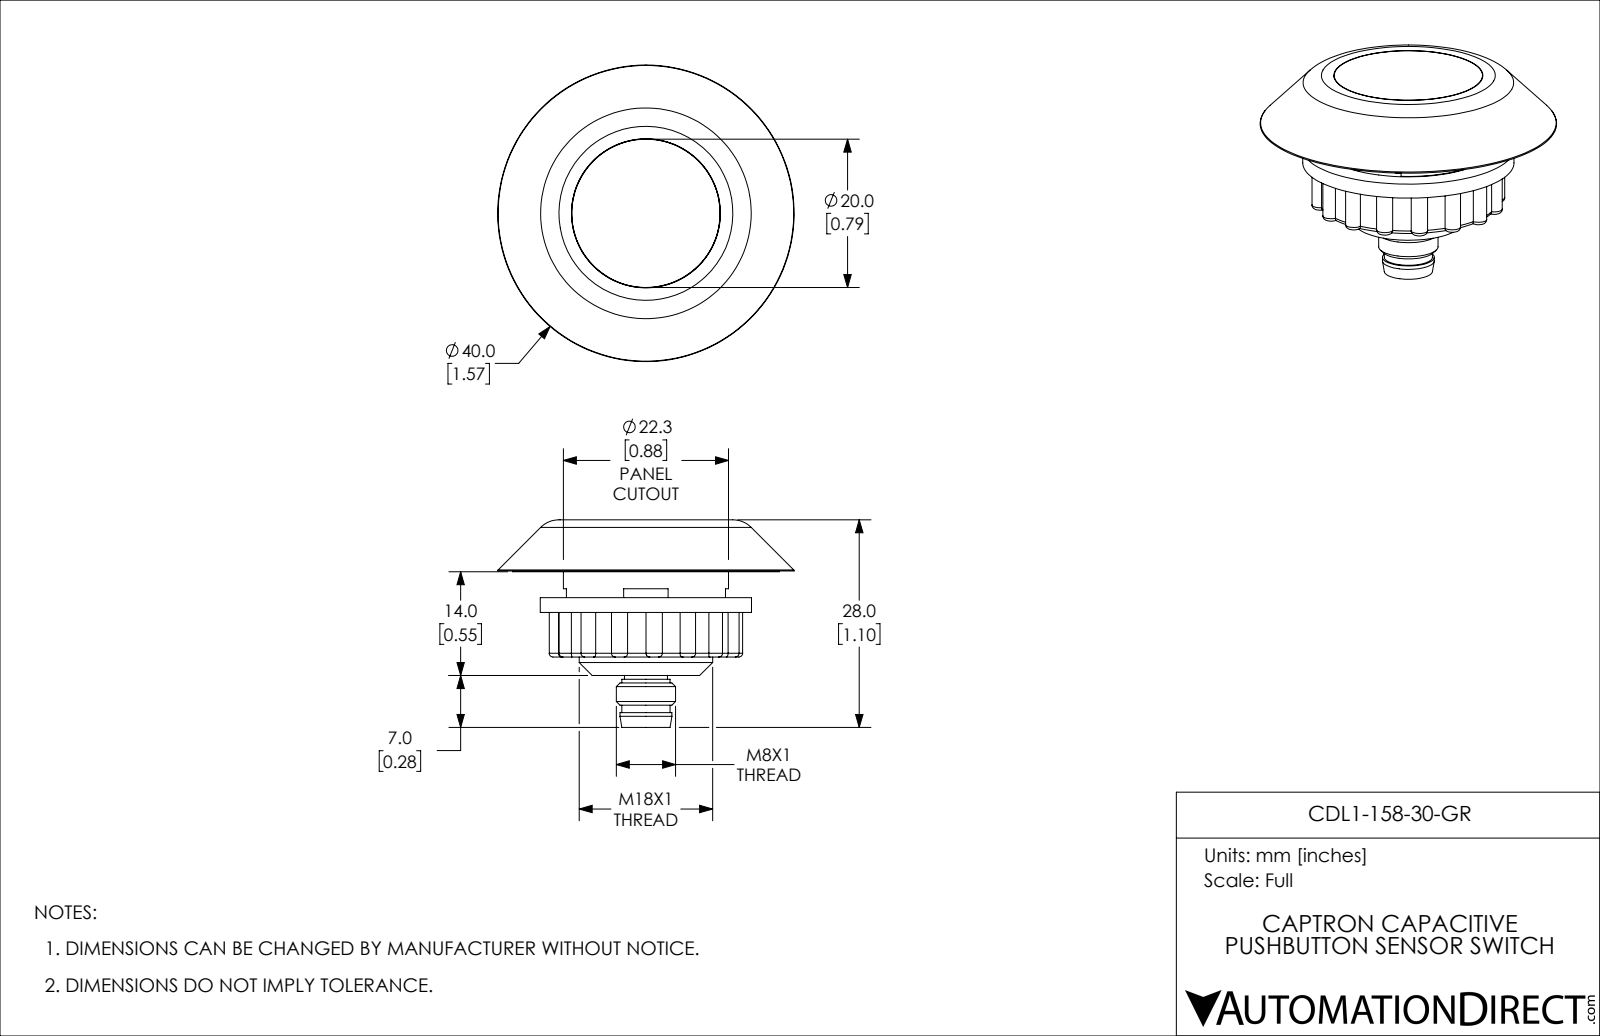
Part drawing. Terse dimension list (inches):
name: CDL1-158-30-GR
written by: SolidWorks 2019 (CONFIG_CONTROL_DESIGN)
unit: in
bodies: 10 solids, 218 faces (40 planar, 99 cylindrical, 79 other)
size: 1.575 × 1.575 × 1.102
volume: 0.659 in³; area: 13.85 in²
holes: 2× ⌀0.079, 1× ⌀0.236, 1× ⌀0.669, 1× ⌀0.791, 1× ⌀0.89, 1× ⌀0.906, 1× ⌀1.457
bosses: 4× ⌀0.039, 1× ⌀1.417, 1× ⌀1.122, 1× ⌀0.877, 1× ⌀0.709, 1× ⌀0.315, 1× ⌀0.276, 1× ⌀0.256
rounds: 16× R0.043, 1× R0.39, 1× R0.472
face distances: 0.118, 0.039, 0.236, 0.157, 0.413, 0.295, 0.276, 0.177, 0.138, 0.492
hole spacings: 0.217, 0.433
